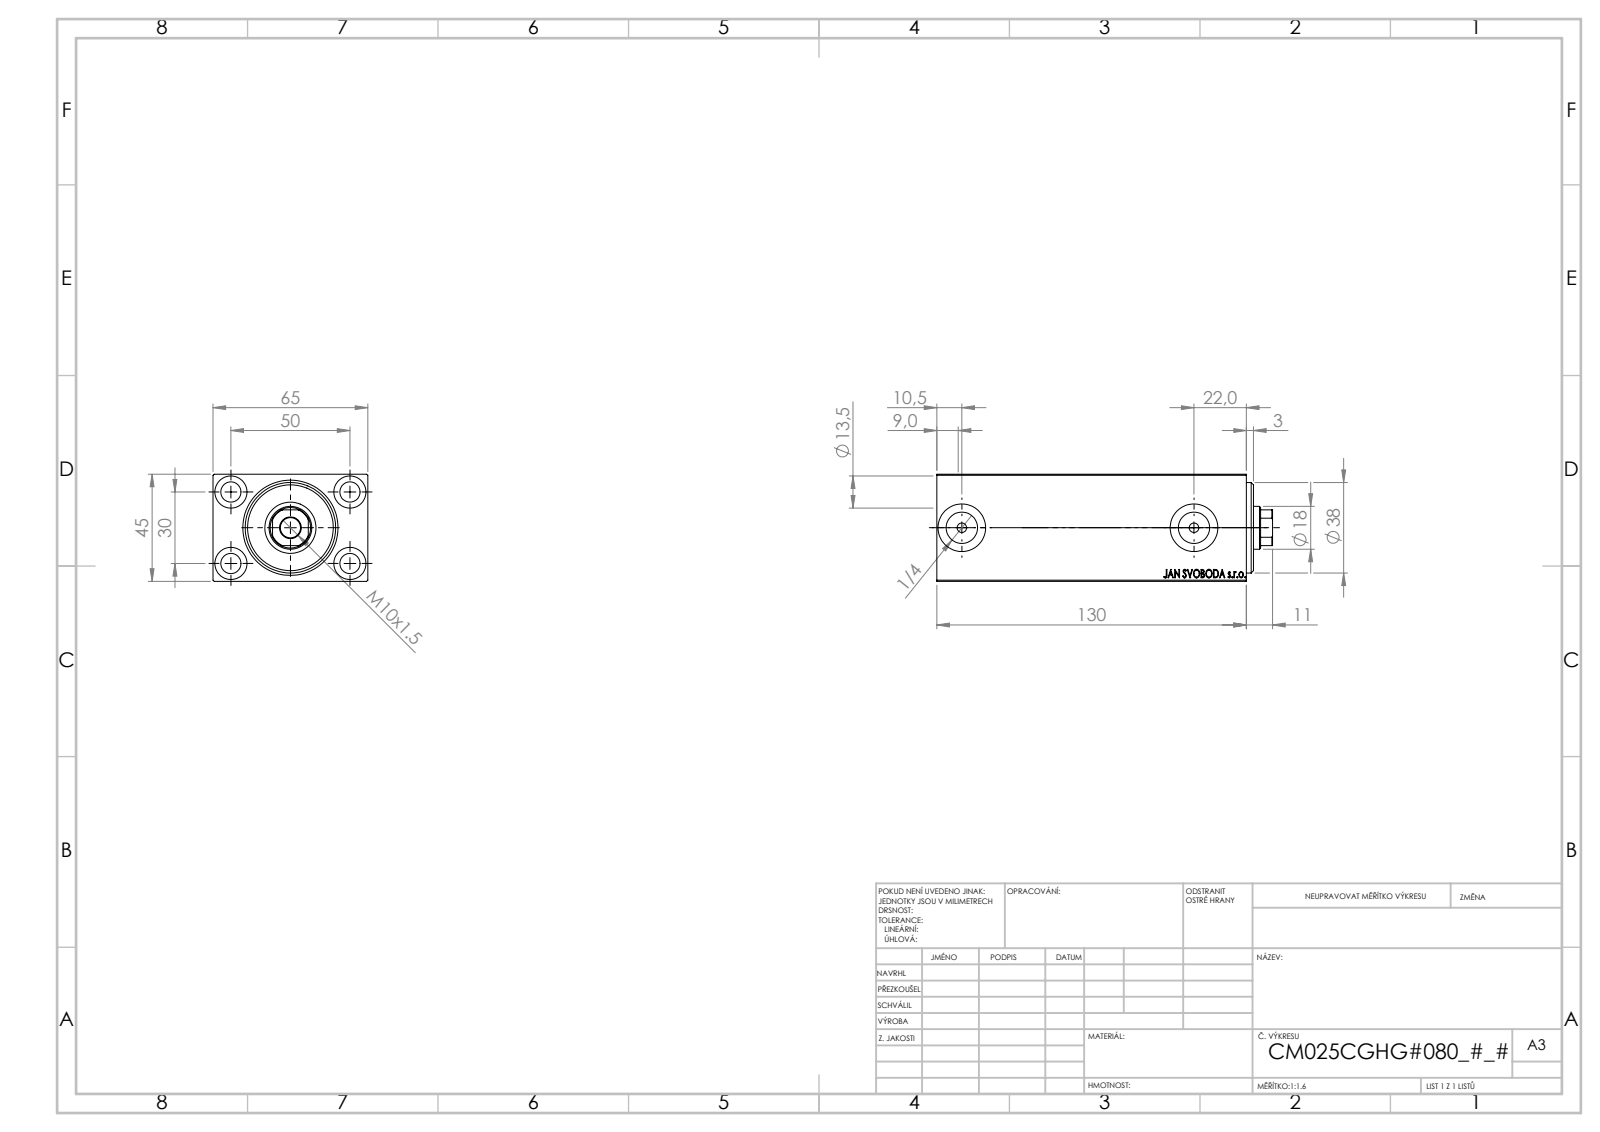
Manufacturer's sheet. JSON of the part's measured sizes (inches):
{"part_name": "V450CM_C_VCP; V450CM_C_Body; V450CM_VC_B", "step_written_by": "SolidWorks 2019 (CONFIG_CONTROL_DESIGN)", "units": "inches", "bodies": {"solids": 3, "faces": 862, "planar": 408, "cylindrical": 60, "other": 394}, "overall_size": [5.551, 2.559, 1.772], "volume_in3": 19.88, "surface_area_in2": 116.8, "round_holes": [[0.335, 5], [0.531, 4], [0.157, 2], [0.518, 2], [0.787, 2], [0.709, 1], [0.846, 1], [0.984, 1], [1.063, 1], [1.496, 1]], "partial_cylinders_radius": [[0.335, 1]], "face_to_face_distances": [1.772, 2.559, 4.882, 4.921, 0.197, 5.118, 0.118, 0.236, 4.685, 0.315], "hole_center_spacings": [1.148, 1.181, 1.969, 2.296, 3.839]}
